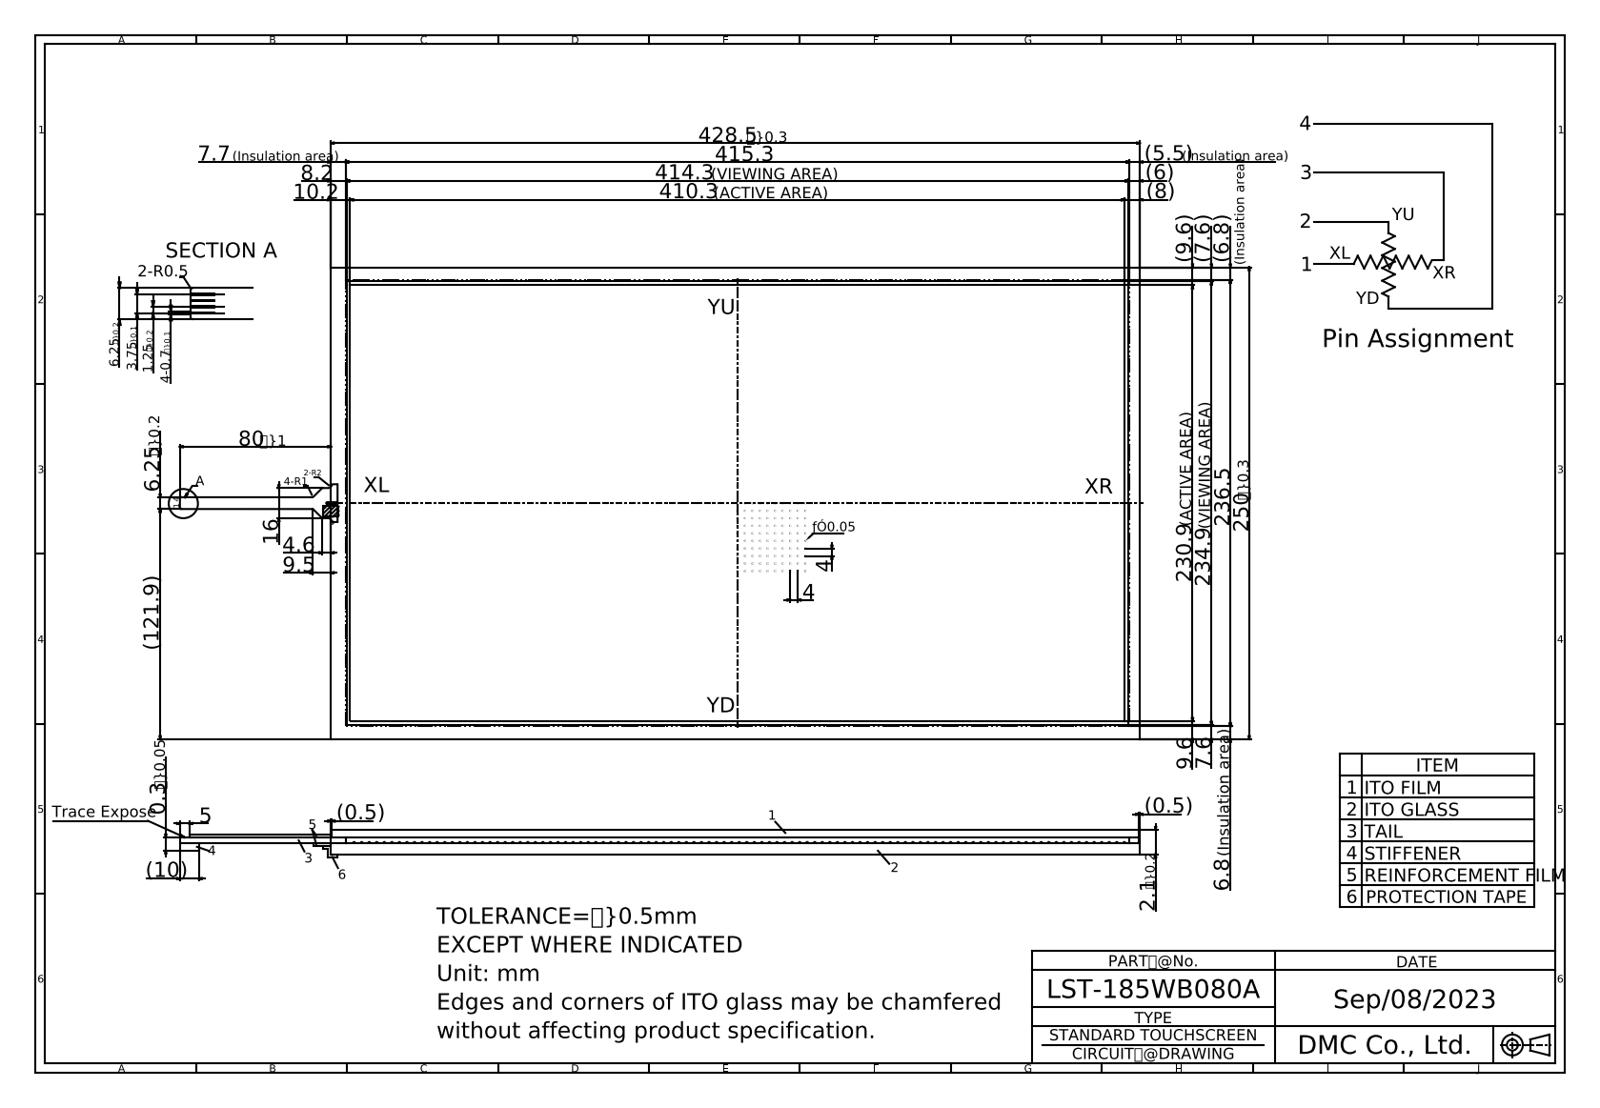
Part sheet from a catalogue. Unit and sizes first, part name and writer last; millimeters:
Units: millimetres
Overall size (bounding box): 508.5 × 250 × 2.1
Partial cylindrical surfaces — rounded edges, fillets, slot ends (radius × count): R1 ×4, R0.5 ×2
Main face-to-face distances: 2.1, 2, 250, 1.91, 428.5, 1.81, 232.9, 1.51, 0.4, 0.49
Volume: 224 777 mm³ · Surface area: 218 520 mm²
Bodies: 1 solid, 51 faces (45 planar, 6 cylindrical, 0 other)
Part name (STEP PRODUCT): LST-185WB080A
STEP written by: Autodesk Inventor 2020 (CONFIG_CONTROL_DESIGN)
